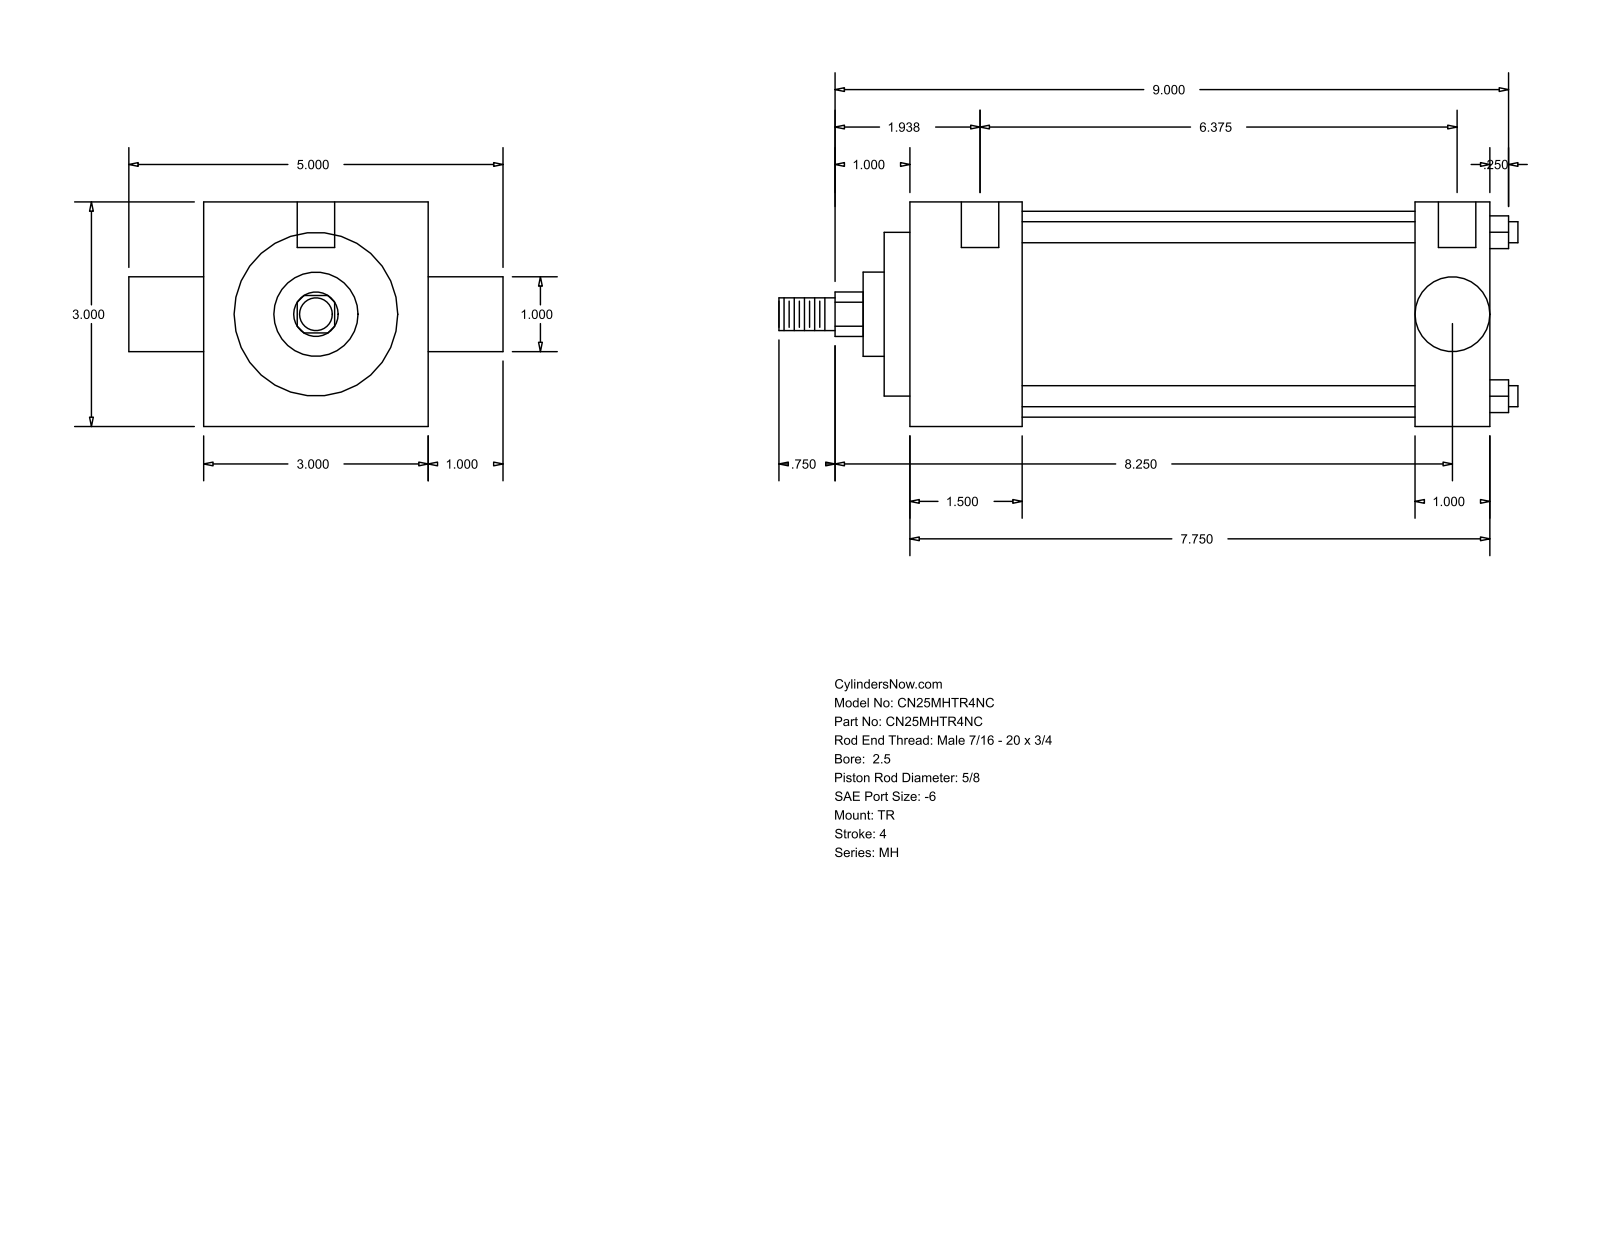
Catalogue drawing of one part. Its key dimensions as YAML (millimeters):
part_name: "MH_TR__0250_0.625"
step_written_by: "GSSL Pune (CONFIG_CONTROL_DESIGN)"
units: millimeters
bodies: {solids: 0, faces: 86, planar: 61, cylindrical: 25, other: 0}
overall_size: [250.82, 127, 76.2]
round_holes:
  - {diameter: 5.56, count: 3}
  - {diameter: 12.7, count: 2}
round_bosses_or_shafts:
  - {diameter: 7.14, count: 4}
  - {diameter: 69.85, count: 1}
  - {diameter: 55.55, count: 1}
  - {diameter: 28.57, count: 1}
  - {diameter: 25.35, count: 1}
  - {diameter: 15.88, count: 1}
  - {diameter: 11.11, count: 1}
partial_cylinders:
  - {radius: 7.54, count: 1}
face_to_face_distances: [76.2, 196.85, 25.4, 38.1, 158.75, 171.45, 133.35, 8.73, 46.83, 180.18]
hole_center_spacings: [3.17, 4.76, 161.93, 165.1, 166.69, 169.86]
